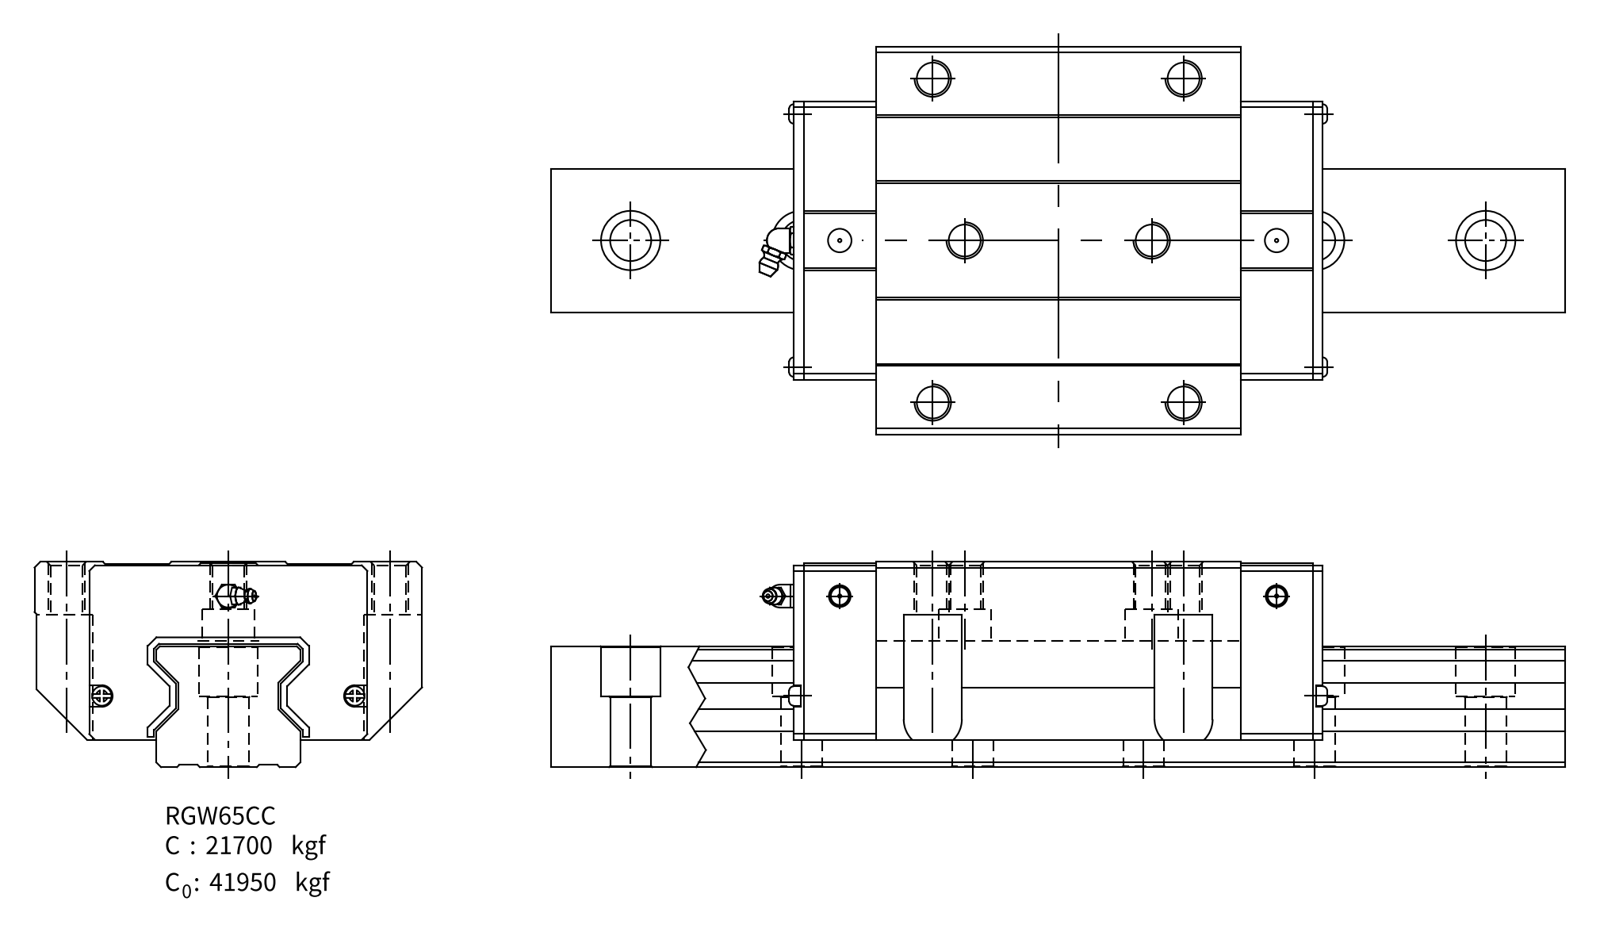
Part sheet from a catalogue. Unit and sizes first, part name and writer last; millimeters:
Units: millimetres
Overall size (bounding box): 370 × 170 × 90
Round holes (diameter × count): ⌀16 ×6, ⌀18 ×5, ⌀26 ×5, ⌀1.5 ×2, ⌀8.5 ×2, ⌀10.3 ×2, ⌀23 ×2, ⌀10 ×1, ⌀12.5 ×1
Partial cylindrical surfaces — rounded edges, fillets, slot ends (radius × count): R11.5 ×4, R1 ×2
Main face-to-face distances: 53.5, 1, 63, 36, 23.36, 37, 89, 41, 78, 9.5
Hole centre spacings: 72.37, 73.76, 75, 81.89, 89.81, 118.6, 119.4, 148.12
Volume: 3 034 000 mm³ · Surface area: 274 661 mm²
Bodies: 2 solids, 199 faces (121 planar, 68 cylindrical, 10 other)
Part name (STEP PRODUCT): RGW65CC_BLOCK_3; RGR65_RAIL_3; RGW65CC_ASM_2_ASM; RGW65CC_ASM
STEP written by: PRO/ENGINEER BY PARAMETRIC TECHNOLOGY CORPORATION, 2004360 (CONFIG_CONTROL_DESIGN)
